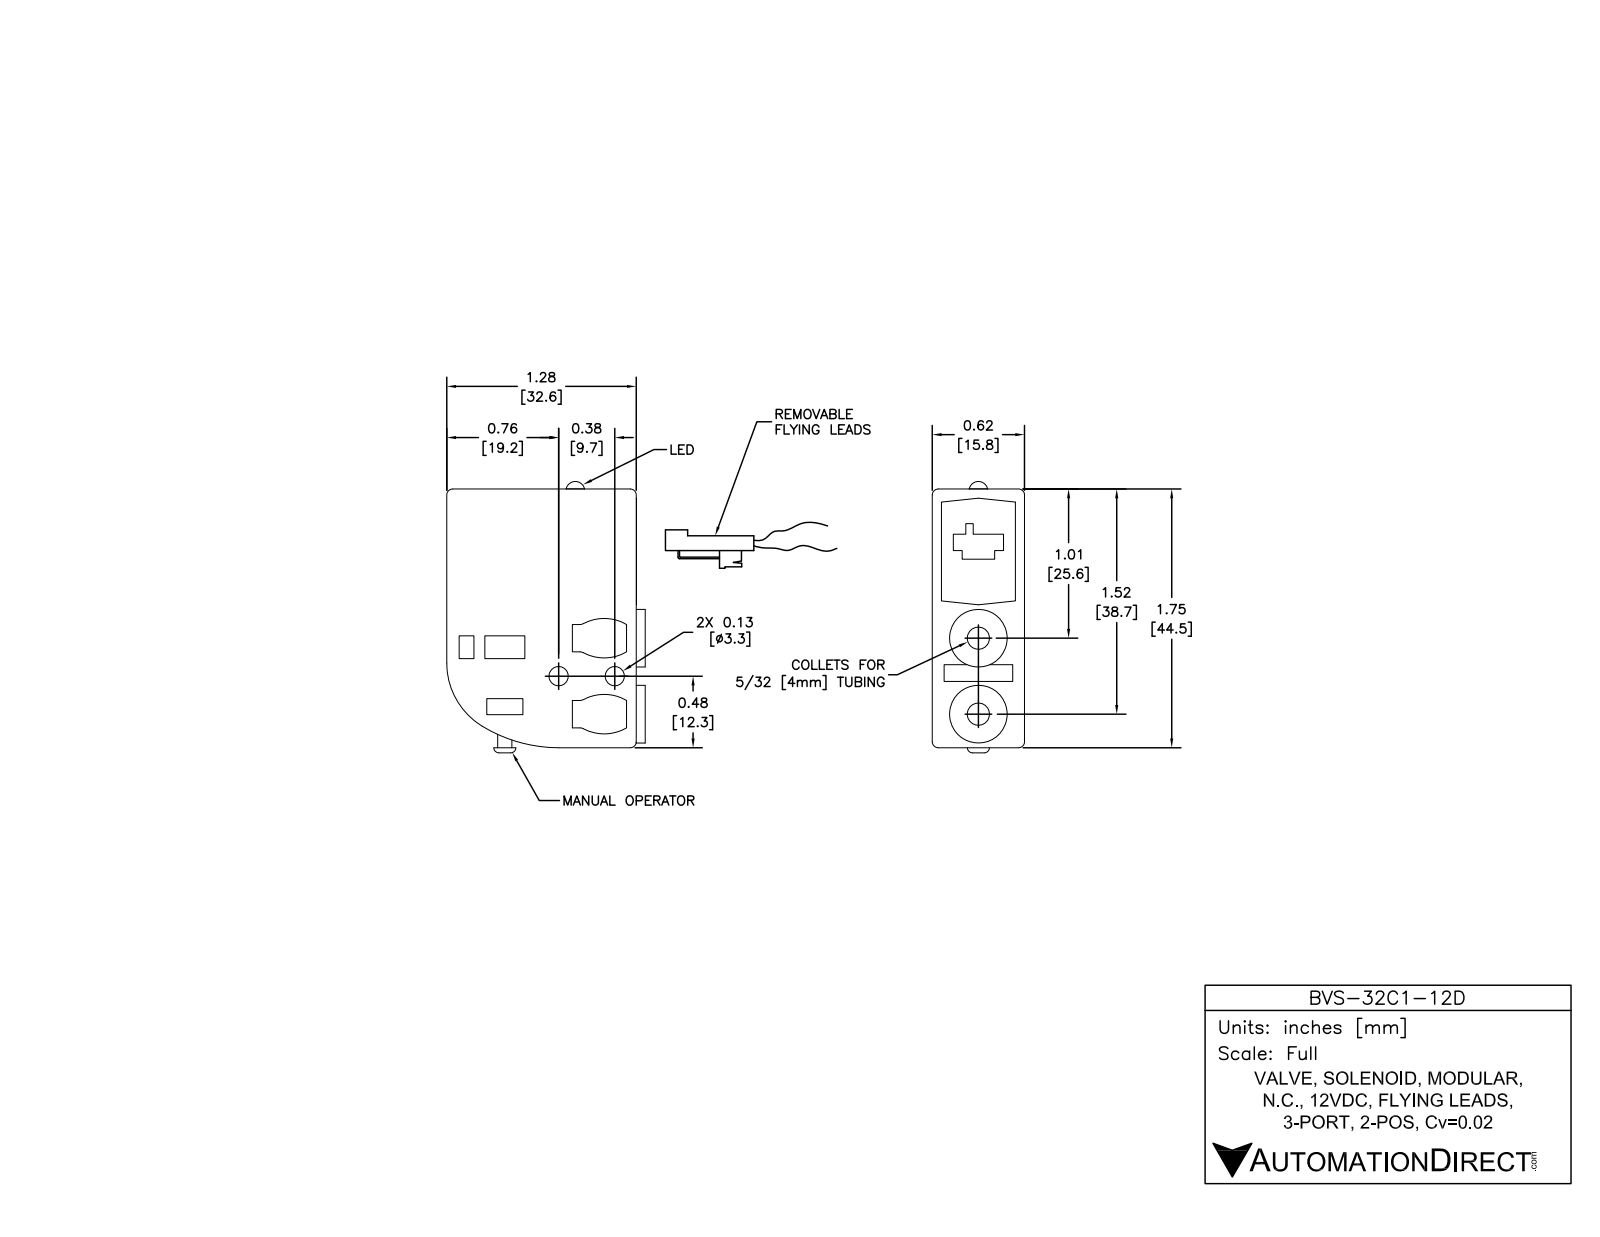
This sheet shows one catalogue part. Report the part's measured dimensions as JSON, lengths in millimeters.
{"part_name": "BVS-32C1-12D", "step_written_by": "SolidWorks 2013 (AUTOMOTIVE_DESIGN)", "units": "millimeters", "bodies": {"solids": 1, "faces": 158, "planar": 93, "cylindrical": 52, "other": 13}, "overall_size": [46.6, 34.2, 15.8], "volume_mm3": 20420, "surface_area_mm2": 6561, "round_holes": [[3.3, 2], [3.8, 2], [6.5, 2], [1.2, 1]], "round_bosses_or_shafts": [[9.9, 2], [3.1, 1], [2.4, 1]], "partial_cylinders_radius": [[1, 11], [1.3, 4], [7.6, 4], [12.7, 1], [25.4, 1]], "face_to_face_distances": [15.8, 2.5, 13.3, 32.7, 32.7, 44.5, 10.8, 1.5, 1.5, 34.2], "hole_center_spacings": [1.5, 9.7, 11.5, 13.1]}
